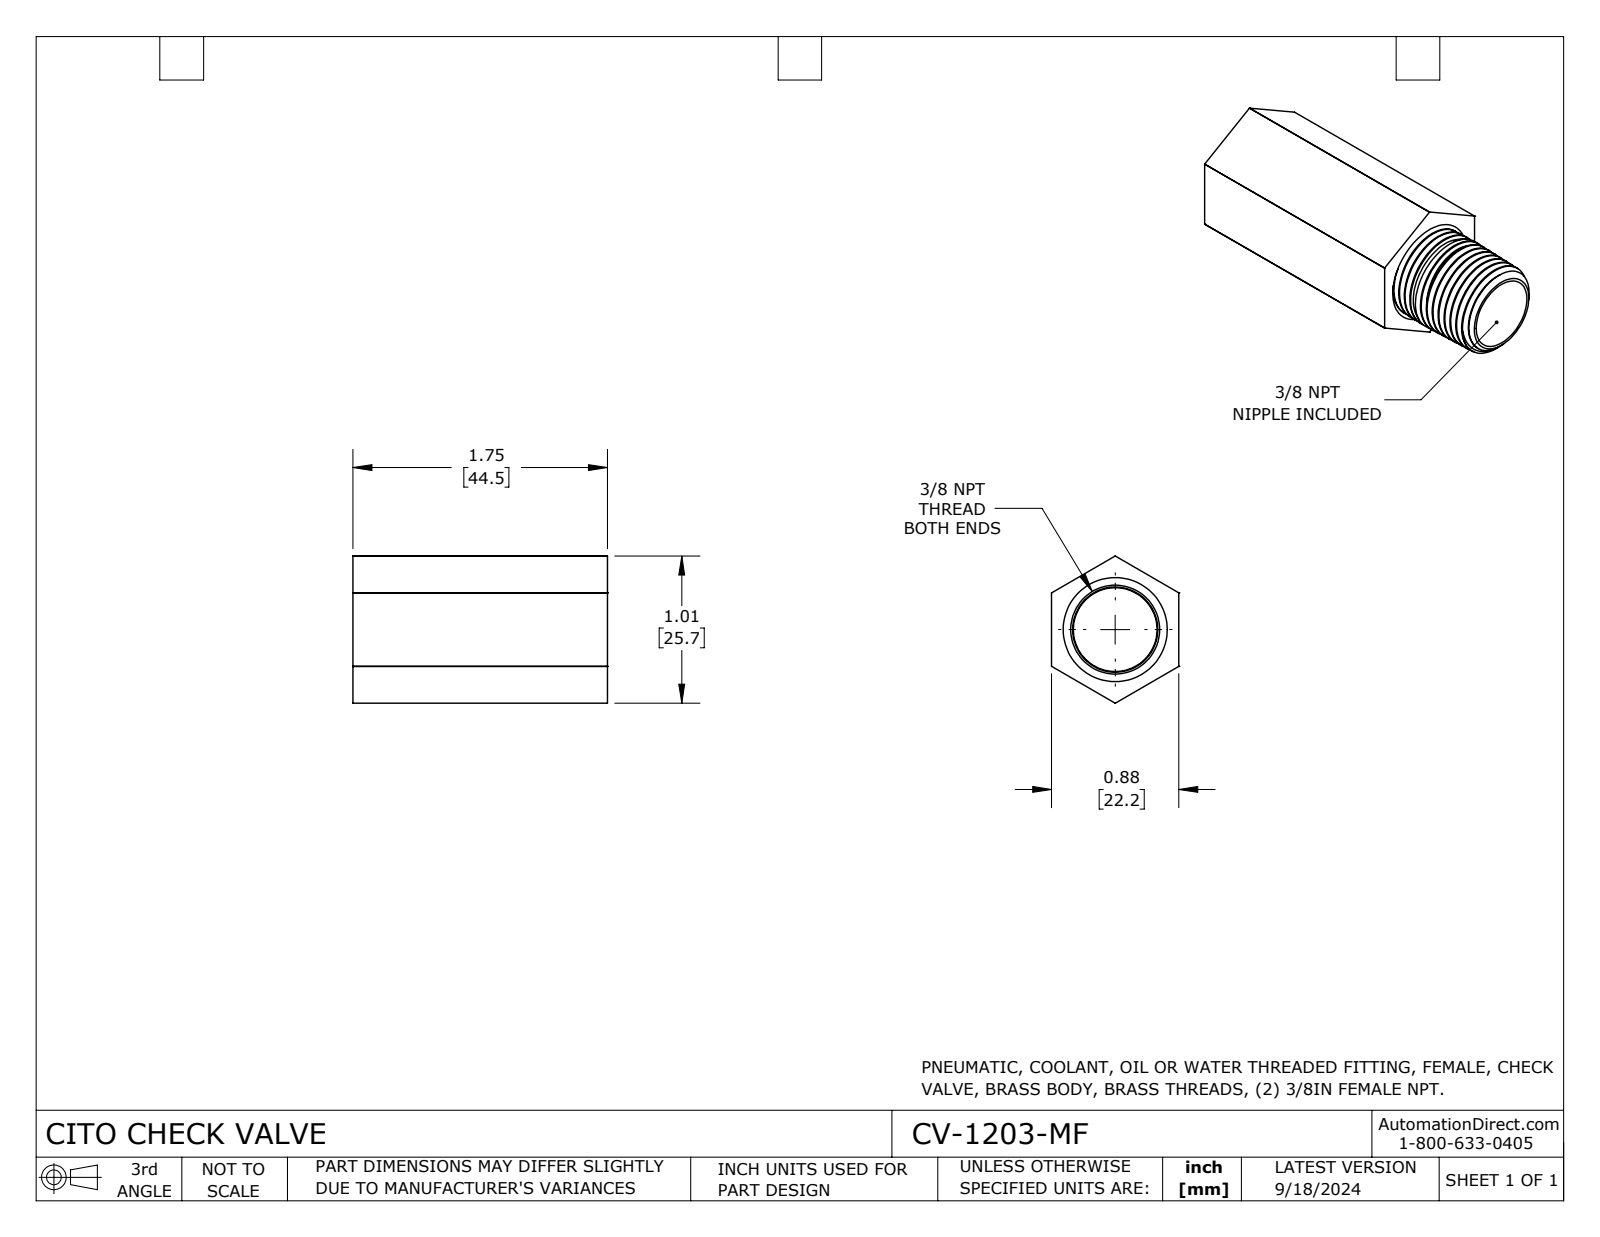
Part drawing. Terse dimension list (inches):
name: CV-1203-MF
written by: SolidWorks 2023 (CONFIG_CONTROL_DESIGN)
unit: in
bodies: 5 solids, 147 faces (41 planar, 60 cylindrical, 46 other)
size: 1.75 × 1.01 × 0.875
volume: 0.688 in³; area: 11.55 in²
holes: 1× ⌀0.046, 1× ⌀0.085, 1× ⌀0.086, 1× ⌀0.125, 1× ⌀0.5, 1× ⌀0.566, 1× ⌀0.578, 1× ⌀0.775
bosses: 1× ⌀0.576, 1× ⌀0.426, 1× ⌀0.25, 1× ⌀0.207, 1× ⌀0.122, 1× ⌀0.082
rounds: 6× R0.004, 6× R0.01, 6× R0.133, 1× R0.243, 1× R0.505
face distances: 0.875, 1.75, 0.966, 0.784, 0.842, 0.124, 0.908, 0.932, 0.091, 0.034
